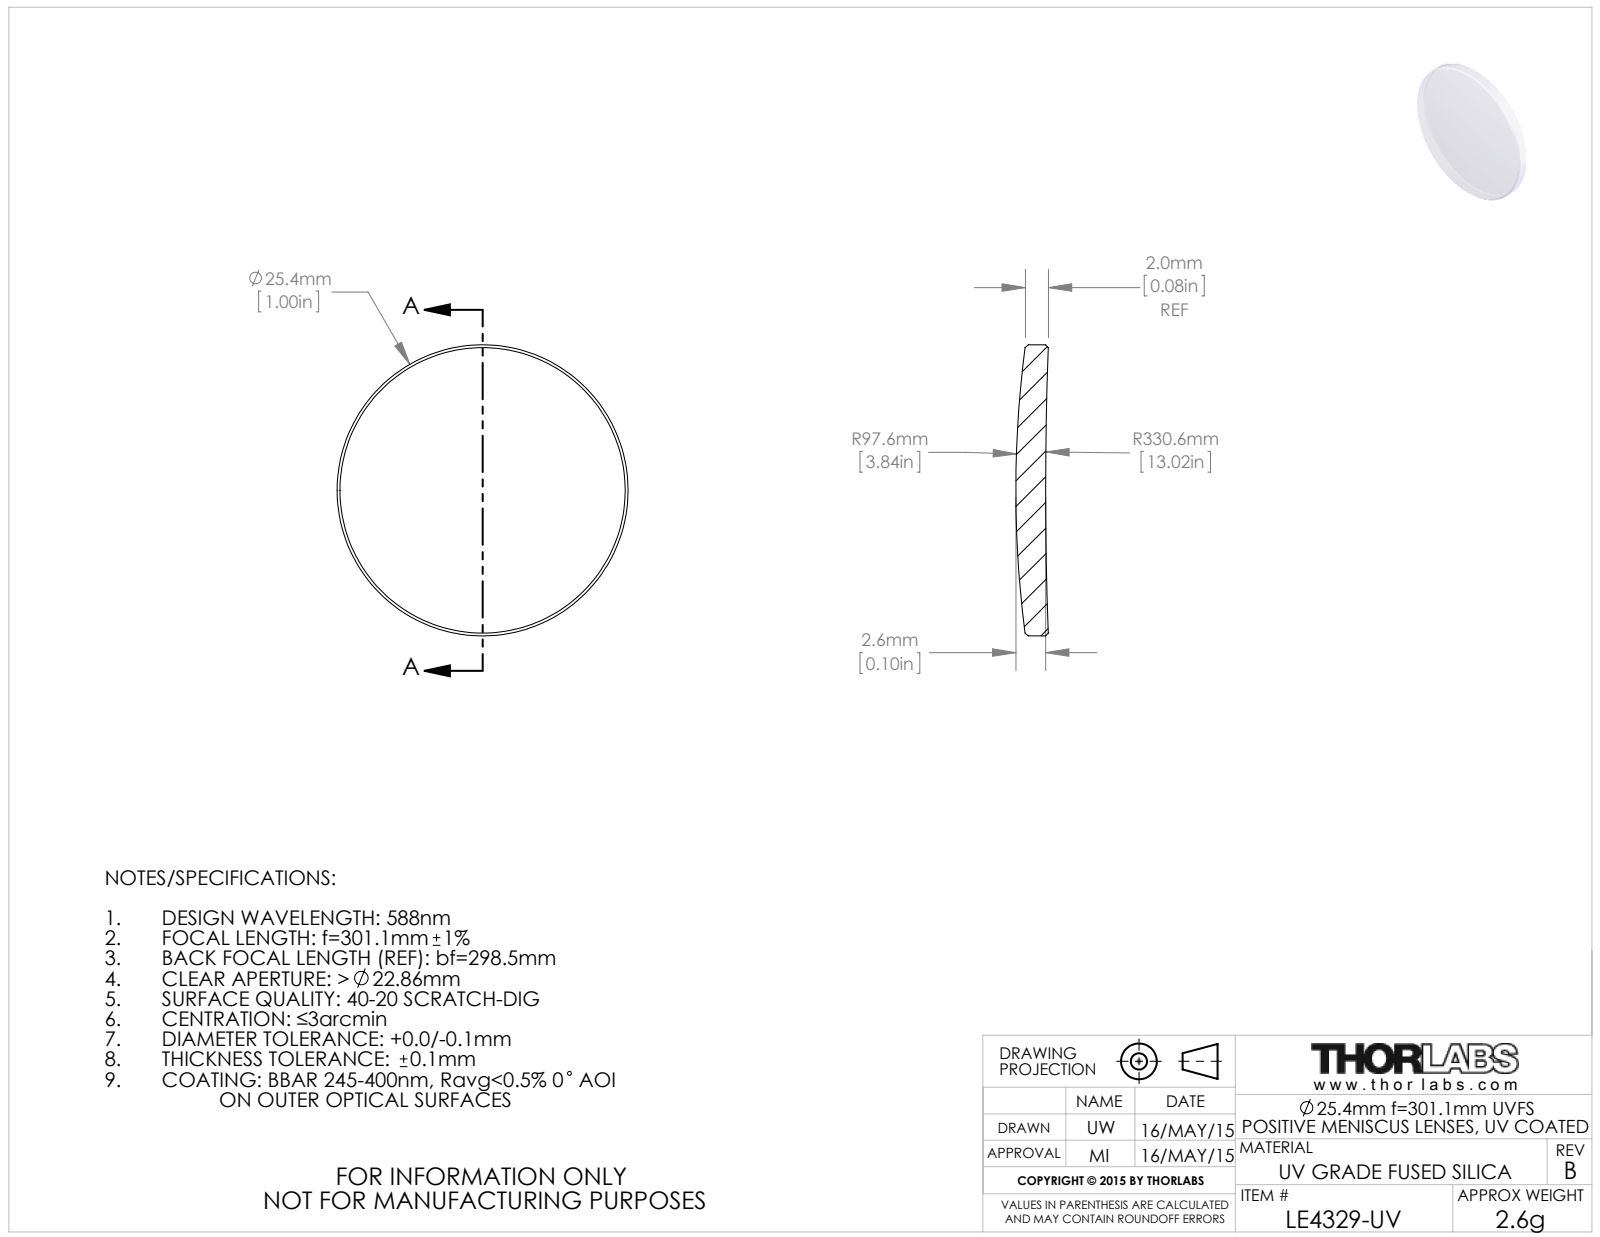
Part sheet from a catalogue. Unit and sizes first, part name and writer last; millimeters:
Units: millimetres
Overall size (bounding box): 25.4 × 25.4 × 2.83
Round bosses / shafts (diameter × count): ⌀25.4 ×1
Volume: 1 164 mm³ · Surface area: 1 154 mm²
Bodies: 1 solid, 10 faces (0 planar, 2 cylindrical, 8 other)
Part name (STEP PRODUCT): 4928-E0W
STEP written by: SolidWorks 2014 (CONFIG_CONTROL_DESIGN)
